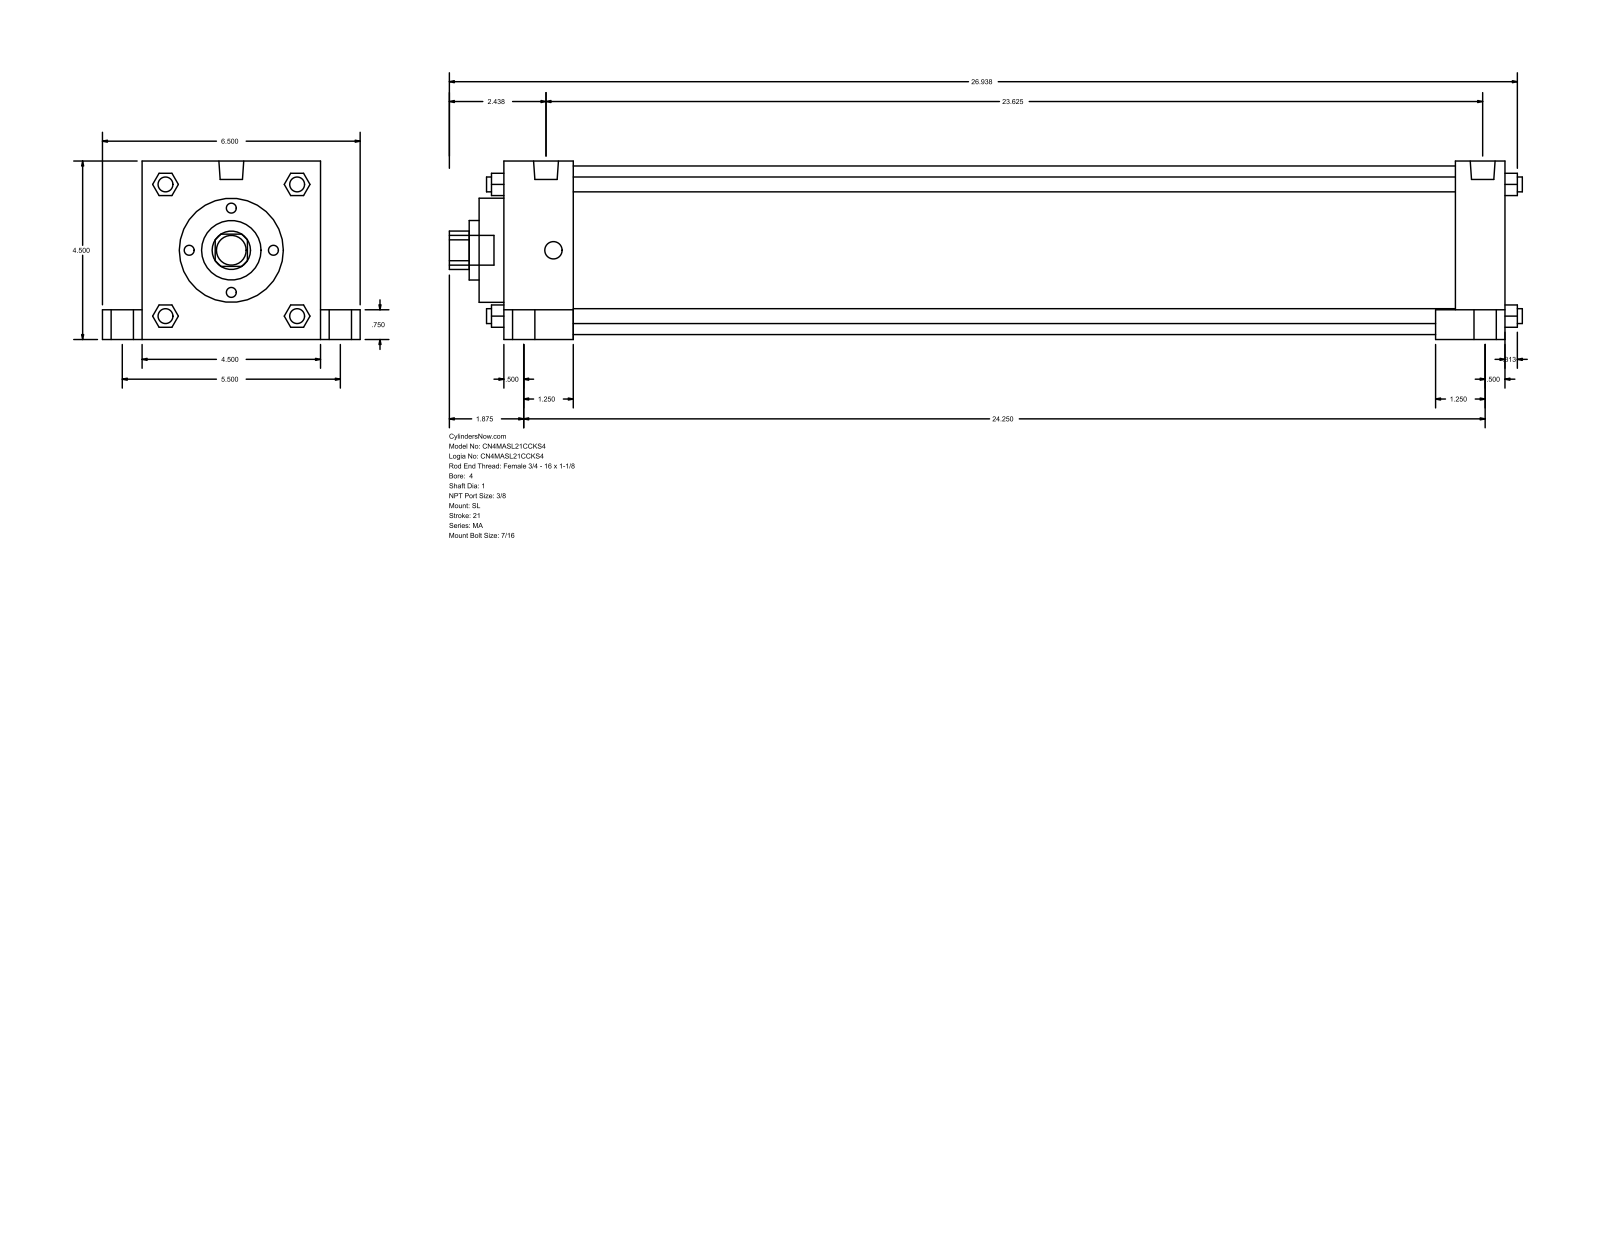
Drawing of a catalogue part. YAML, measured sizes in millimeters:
part_name: "MA_SL__0400_1"
step_written_by: "GSSL Pune (CONFIG_CONTROL_DESIGN)"
units: millimeters
bodies: {solids: 0, faces: 150, planar: 113, cylindrical: 37, other: 0}
overall_size: [687.39, 165.1, 114.3]
round_holes:
  - {diameter: 25.4, count: 1}
  - {diameter: 38.1, count: 1}
  - {diameter: 66.67, count: 1}
  - {diameter: 107.95, count: 1}
round_bosses_or_shafts:
  - {diameter: 20.64, count: 4}
  - {diameter: 14.29, count: 4}
  - {diameter: 11.11, count: 4}
  - {diameter: 9.53, count: 4}
  - {diameter: 15.93, count: 2}
  - {diameter: 19.05, count: 1}
partial_cylinders:
  - {radius: 12.29, count: 1}
face_to_face_distances: [114.3, 641.35, 44.46, 596.89, 609.6, 565.14, 31.75, 25.4, 139.7, 657.22]
